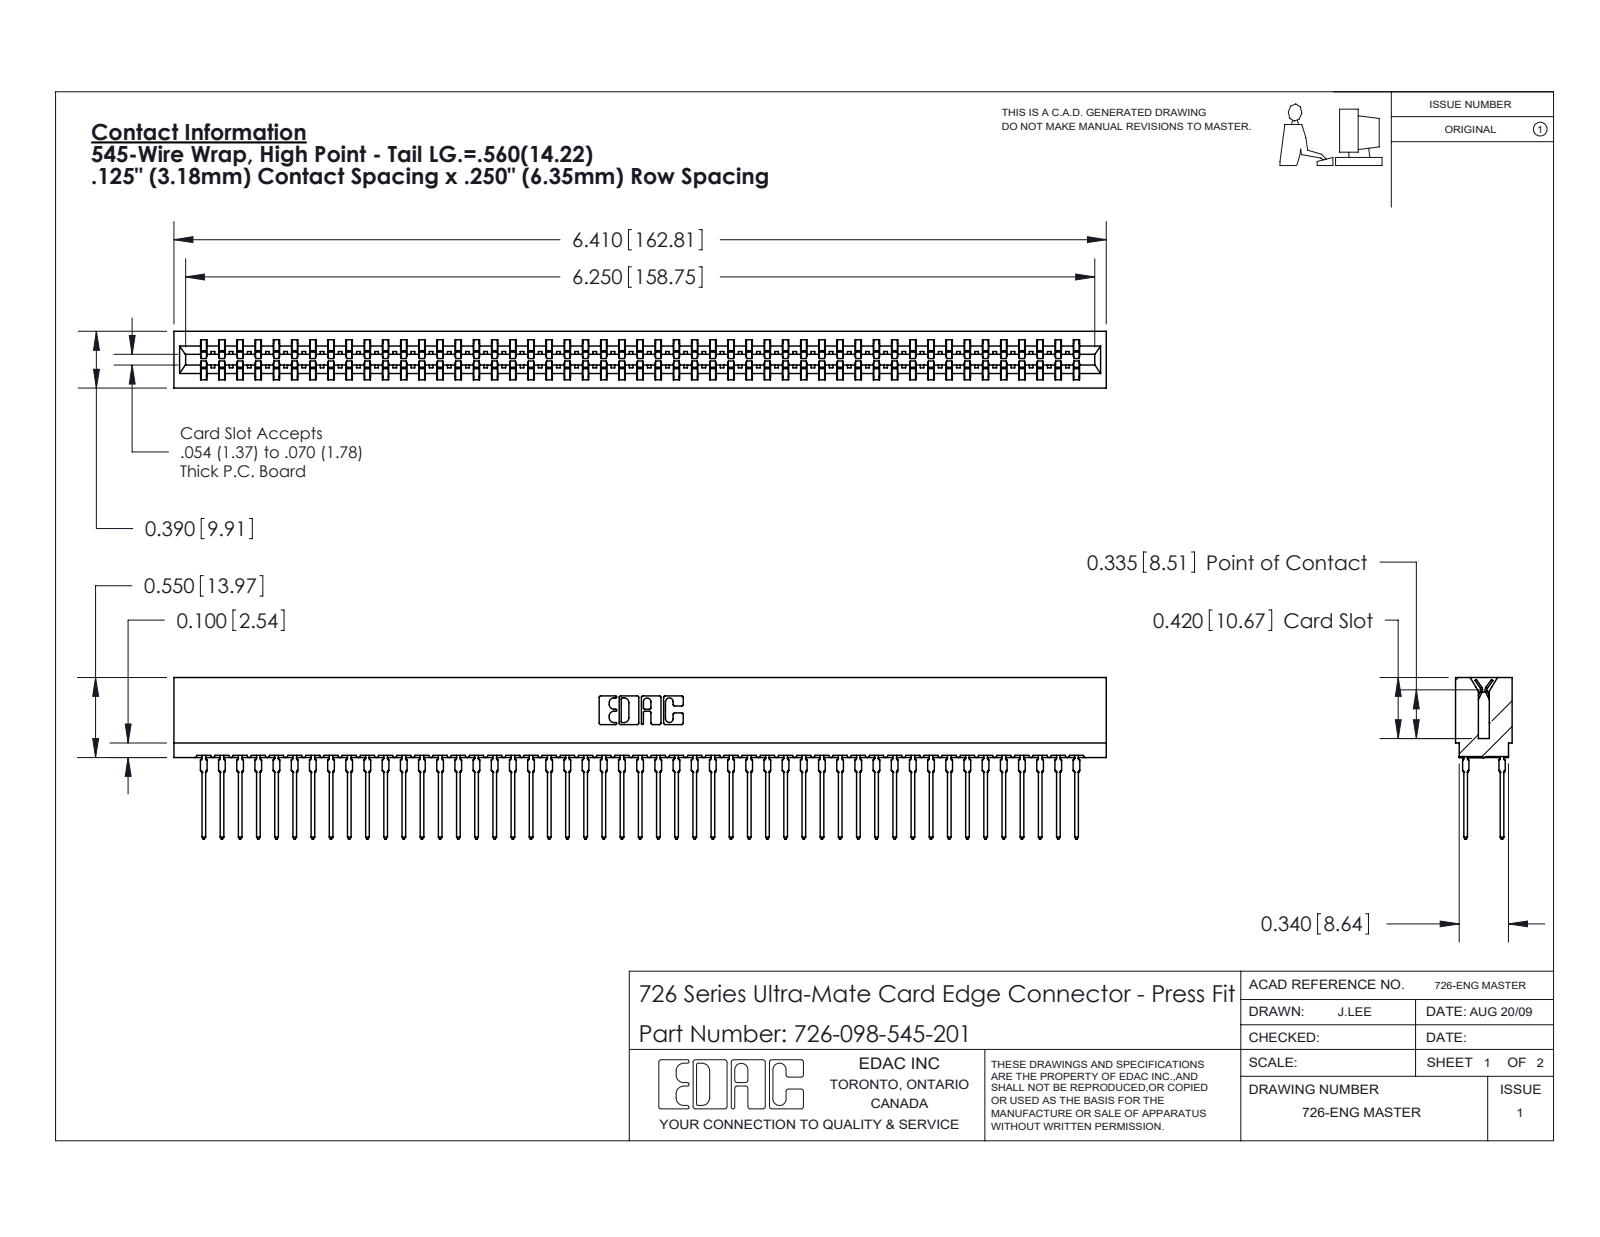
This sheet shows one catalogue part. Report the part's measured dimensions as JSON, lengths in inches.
{"part_name": "726 Part_.515 Slot Depth - 01; 726-098-545-201; 746-292-001_545", "step_written_by": "SolidWorks 2020 (CONFIG_CONTROL_DESIGN)", "units": "inches", "bodies": {"solids": 99, "faces": 8868, "planar": 4563, "cylindrical": 1757, "other": 2548}, "overall_size": [6.41, 1.109, 0.39], "volume_in3": 0.933, "surface_area_in2": 42.1, "partial_cylinders_radius": [[0.021, 196], [0.015, 50], [0.01, 22], [0.005, 8], [0.011, 8], [0.007, 6], [0.031, 6], [0.026, 3]], "face_to_face_distances": [0.057, 0.333, 0.025, 0.307, 0.39, 0.25, 0.275, 0.083, 0.365, 0.032]}
